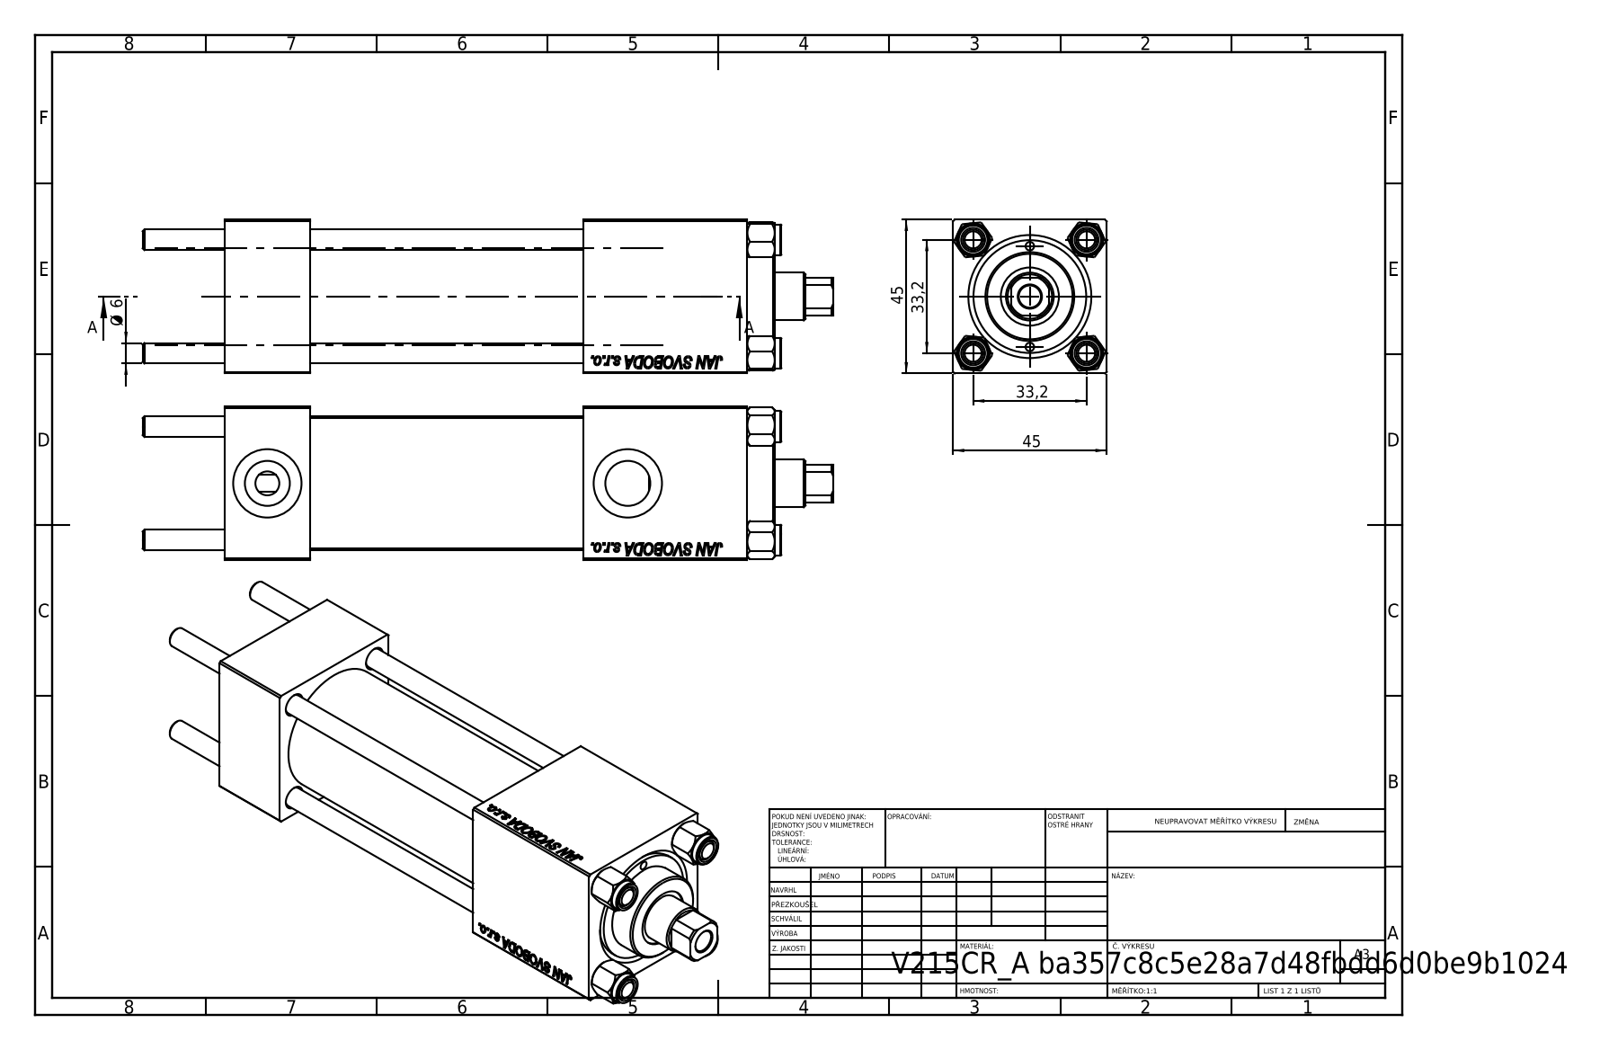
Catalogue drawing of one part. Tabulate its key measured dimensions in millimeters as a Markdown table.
| quantity | value |
| --- | --- |
| part name | V215CR_VCP; NUT_M5; V215CR_BODY_A; CR025_012_A_0_G_A_G_M_020_+#_##_TYCINKA (+1 more) |
| STEP written by | SolidWorks 2019 (CONFIG_CONTROL_DESIGN) |
| units | millimeters |
| bodies | 11 solids, 1139 faces (521 planar, 82 cylindrical, 536 other) |
| overall size | 202 × 45 × 45 |
| volume | 216 169 mm³ |
| surface area | 83 081 mm² |
| round holes (diameter × count) | 6 × 4, 2.5 × 2, 7 × 2, 13.16 × 2, 20 × 2, 6.5 × 1, 14 × 1, 17 × 1, 24 × 1, 32 × 1, 33 × 1 |
| round bosses / shafts (diameter × count) | 9 × 4, 38 × 1, 26 × 1 |
| partial cylindrical surfaces (radius × count) | 6.5 × 1 |
| main face-to-face distances | 45, 25, 153, 128, 105, 80, 48, 124.3, 99.3, 19.3 |
| hole center spacings | 16.7, 23.48, 33.2, 35.47, 14.75, 46.95, 29.5, 105.5 |
